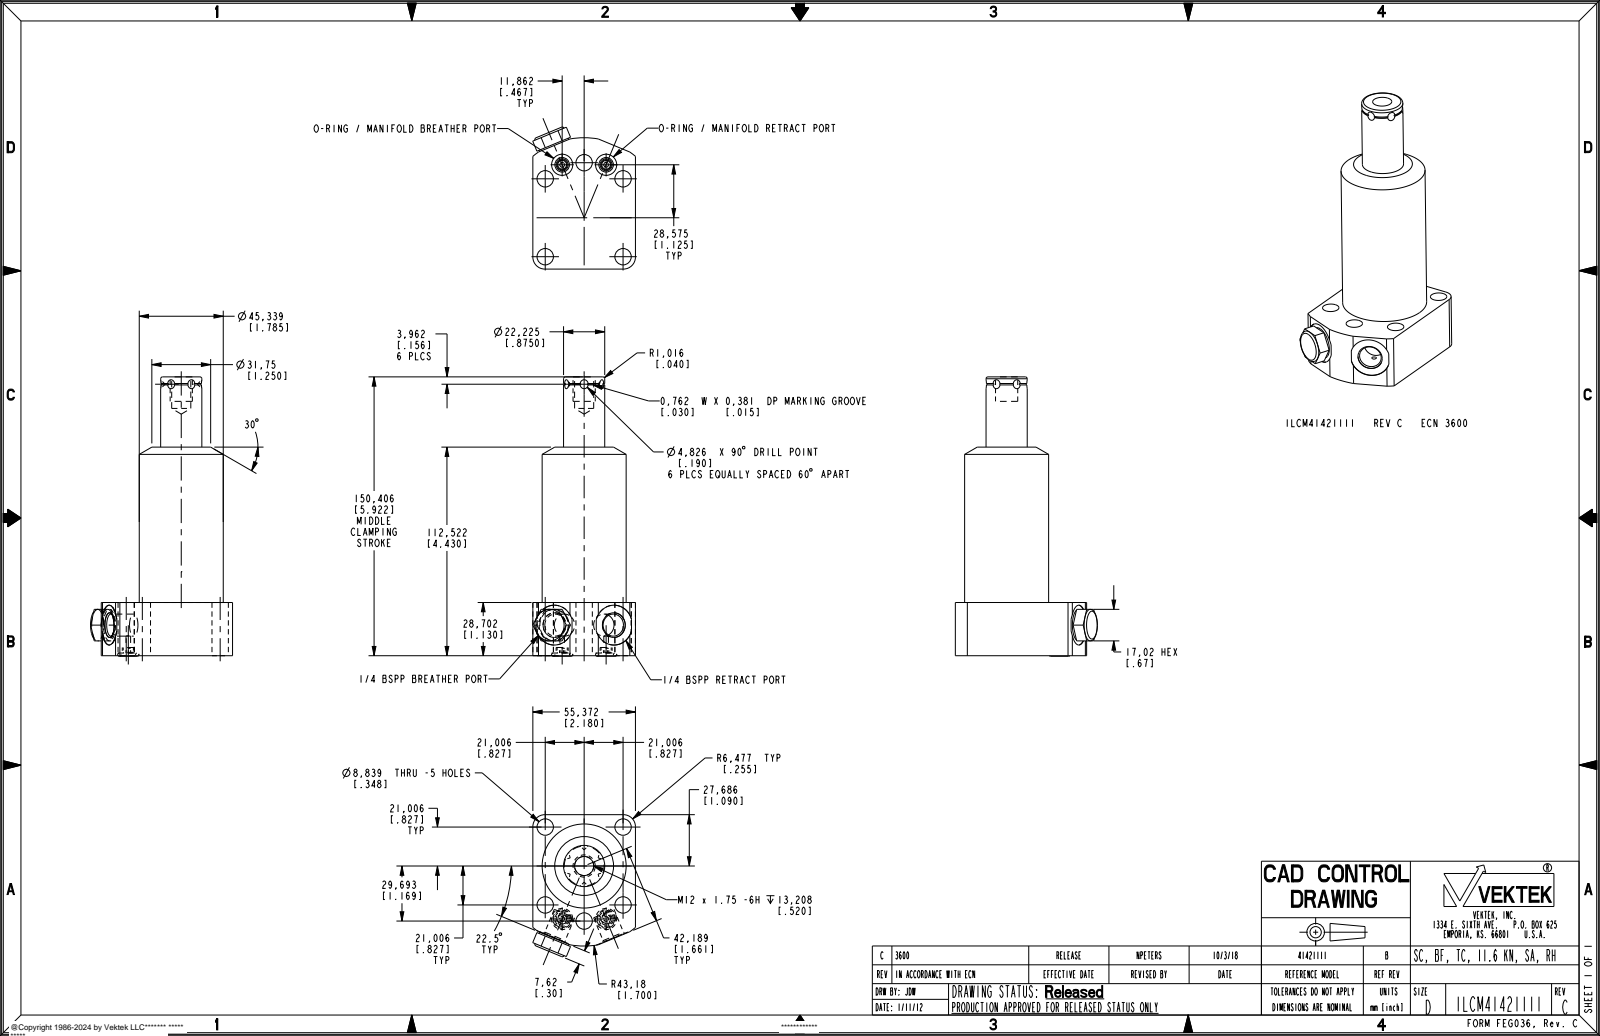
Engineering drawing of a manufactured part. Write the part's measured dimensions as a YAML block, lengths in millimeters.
part_name: "ILCM41421111"
step_written_by: "PRO/ENGINEER BY PARAMETRIC TECHNOLOGY CORPORATION, 2013320 (AUTOMOTIVE_DESIGN)"
units: millimeters
bodies: {solids: 1, faces: 165, planar: 72, cylindrical: 61, other: 32}
overall_size: [150.71, 76.65, 55.44]
volume: 242528
surface_area: 35264
round_holes:
  - {diameter: 8.84, count: 5}
  - {diameter: 2.49, count: 2}
  - {diameter: 6.5, count: 2}
  - {diameter: 11.4, count: 2}
  - {diameter: 11.89, count: 2}
  - {diameter: 13.31, count: 2}
  - {diameter: 21.5, count: 2}
  - {diameter: 10.31, count: 1}
round_bosses_or_shafts:
  - {diameter: 5.49, count: 2}
  - {diameter: 45.34, count: 1}
  - {diameter: 22.23, count: 1}
  - {diameter: 17.02, count: 1}
  - {diameter: 11.99, count: 1}
partial_cylinders:
  - {radius: 6.48, count: 2}
  - {radius: 10.73, count: 1}
  - {radius: 43.18, count: 1}
face_to_face_distances: [28.7, 55.38, 112.52, 83.82, 150.4, 121.7, 37.88, 14.43, 14.17, 7.62]
hole_center_spacings: [29.71, 42.02, 11.87, 11.91, 22.73, 30.93, 33.73, 50.42]
